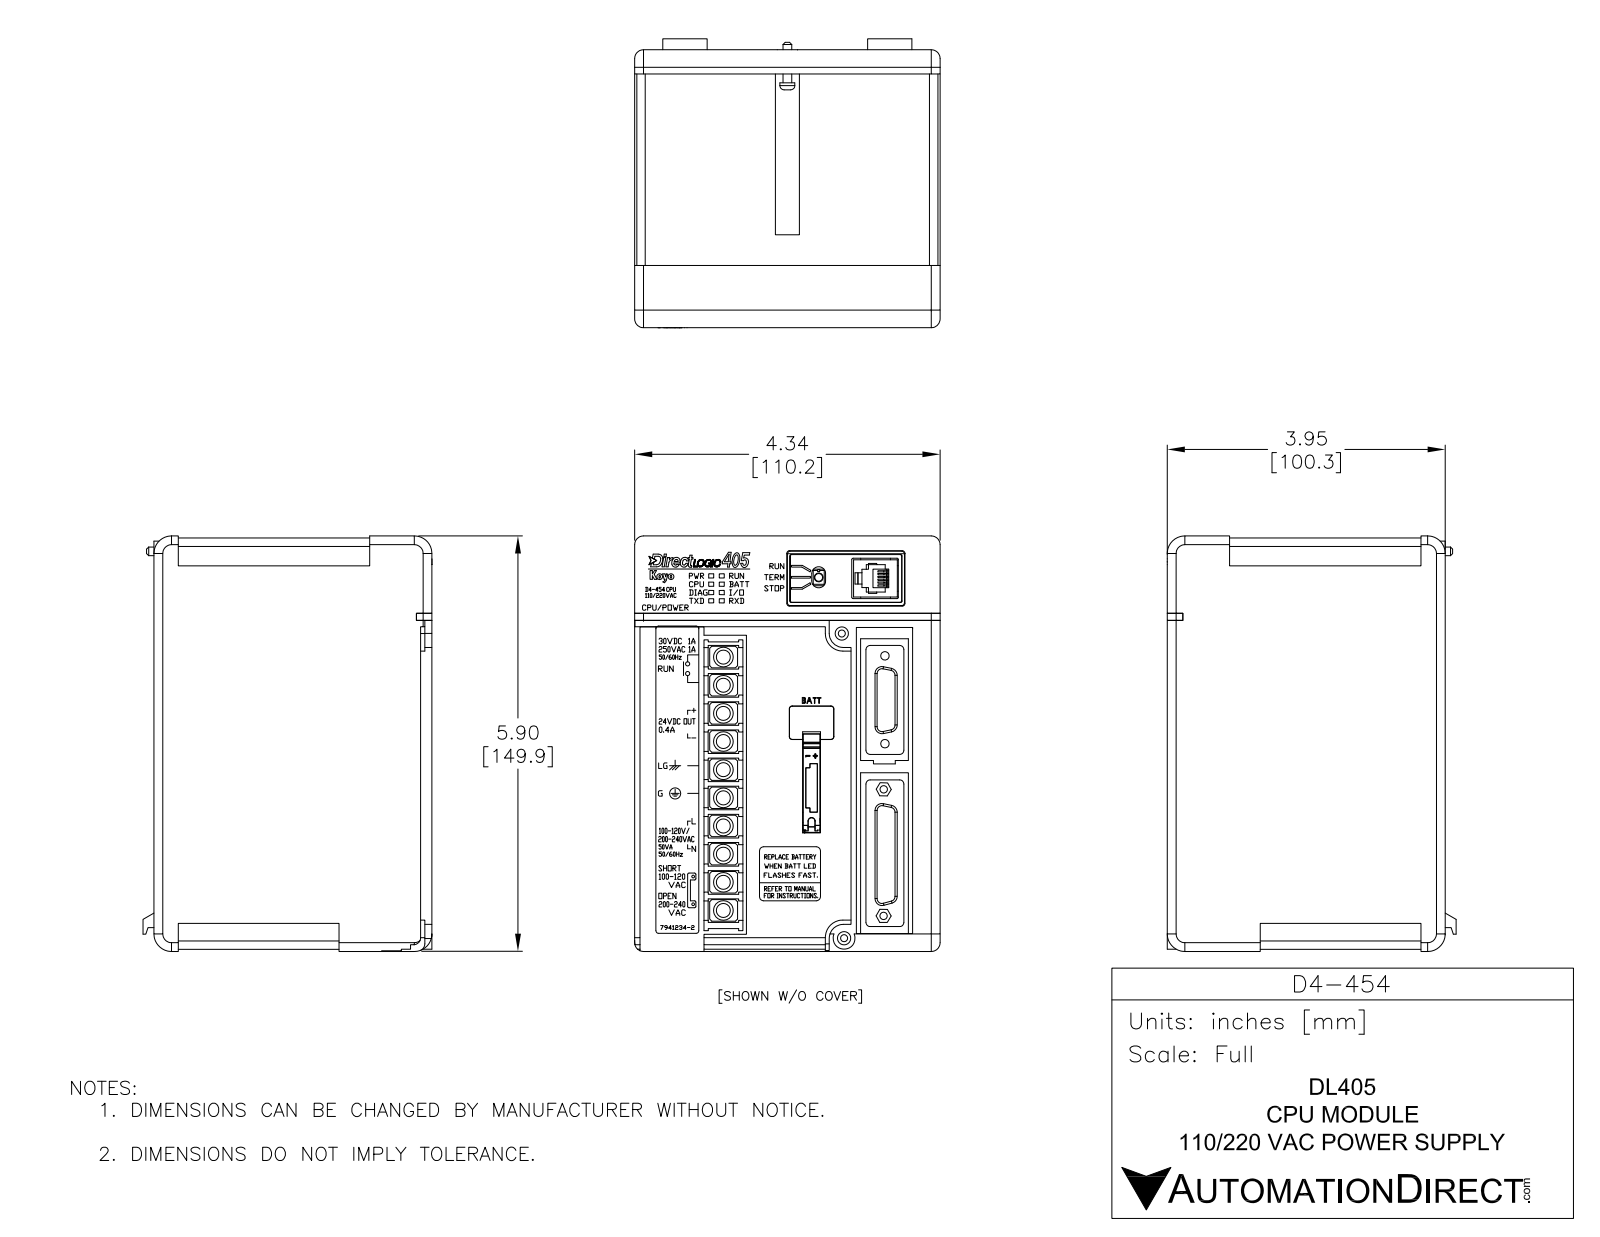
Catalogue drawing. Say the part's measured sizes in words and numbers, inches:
The part is named "D4-454". Its 3-D file was written by "SolidWorks 2016 (AUTOMOTIVE_DESIGN)". It is 9 solids with 5483 faces: 5021 planar, 399 cylindrical and 63 other. Overall it measures 5.905 by 4.34 by 4.107 inches. Its volume is 0.11 cubic inches and its surface area 211.4 square inches. Round holes: 2 of diameter 0.035, 2 of diameter 0.055, 2 of diameter 0.1, 2 of diameter 0.12, 1 of diameter 0.104, 1 of diameter 0.105, 1 of diameter 0.126, 1 of diameter 0.153, 1 of diameter 0.188, 1 of diameter 0.188. Round bosses or shafts: 10 of diameter 0.279, 2 of diameter 0.082, 2 of diameter 0.063, 2 of diameter 0.043, 1 of diameter 0.212, 1 of diameter 0.161, 1 of diameter 0.123. Partial cylindrical surfaces (rounded edges, fillets, slot ends): 19 of radius 0.05, 12 of radius 0.039, 10 of radius 0.099, 10 of radius 0.101, 9 of radius 0.1, 9 of radius 0.125, 8 of radius 0.035, 8 of radius 0.06. The main face-to-face distances are 4.34, 0.03, 5.48, 5.875, 0.425, 5.905, 0.28, 5.2, 5.625, 0.395. The hole center spacings are 0.138, 0.394, 0.644, 0.649, 0.69, 0.816, 1.209, 1.248.
